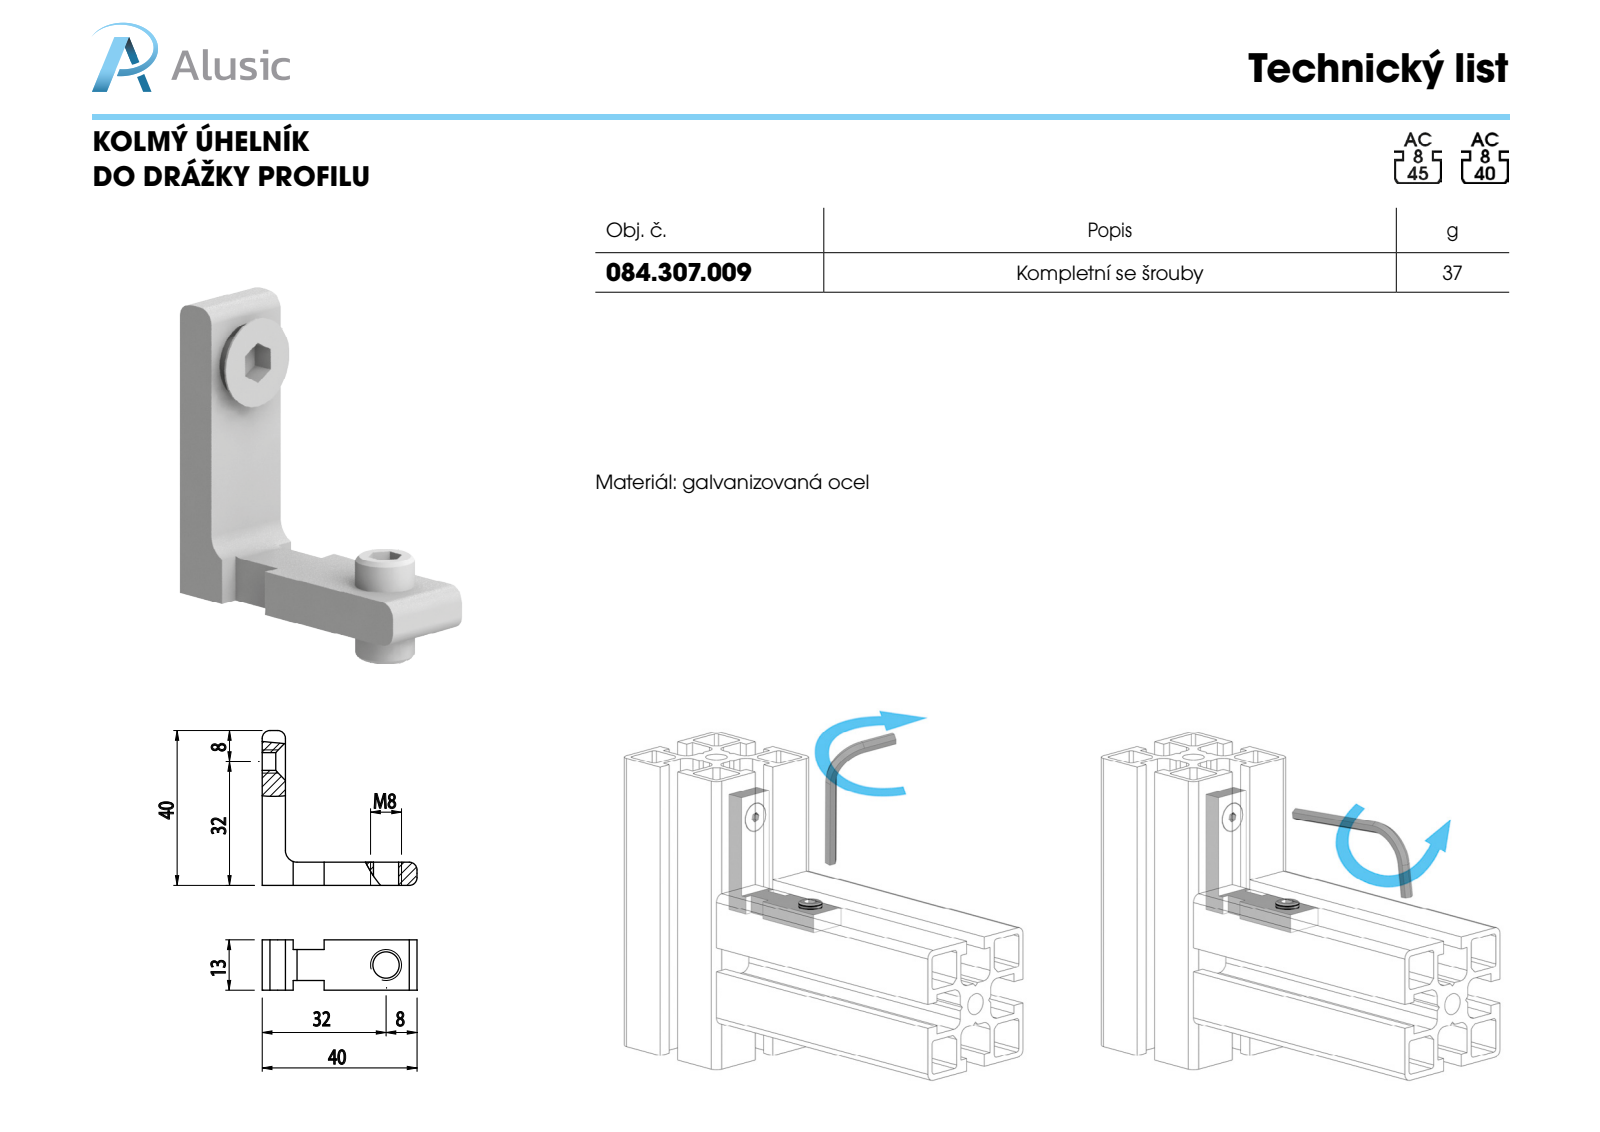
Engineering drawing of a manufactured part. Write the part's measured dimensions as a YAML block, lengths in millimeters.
part_name: "VITI TSEI UNI 5933_M6x10 UNI 5933; GRANI A PUNTA PIATTA UNI 5923_M8X14; 084.307.009"
step_written_by: "SolidWorks 2016 (CONFIG_CONTROL_DESIGN)"
units: millimeters
bodies: {solids: 3, faces: 59, planar: 34, cylindrical: 15, other: 10}
overall_size: [44.01, 41.79, 13]
volume: 6111
surface_area: 3902
round_holes:
  - {diameter: 5, count: 1}
  - {diameter: 6.8, count: 1}
round_bosses_or_shafts:
  - {diameter: 12, count: 1}
  - {diameter: 8, count: 1}
  - {diameter: 6, count: 1}
partial_cylinders:
  - {radius: 2, count: 4}
  - {radius: 3, count: 1}
face_to_face_distances: [6, 13, 10, 8, 2.5, 10.5, 8.21, 2.21, 4, 40]
